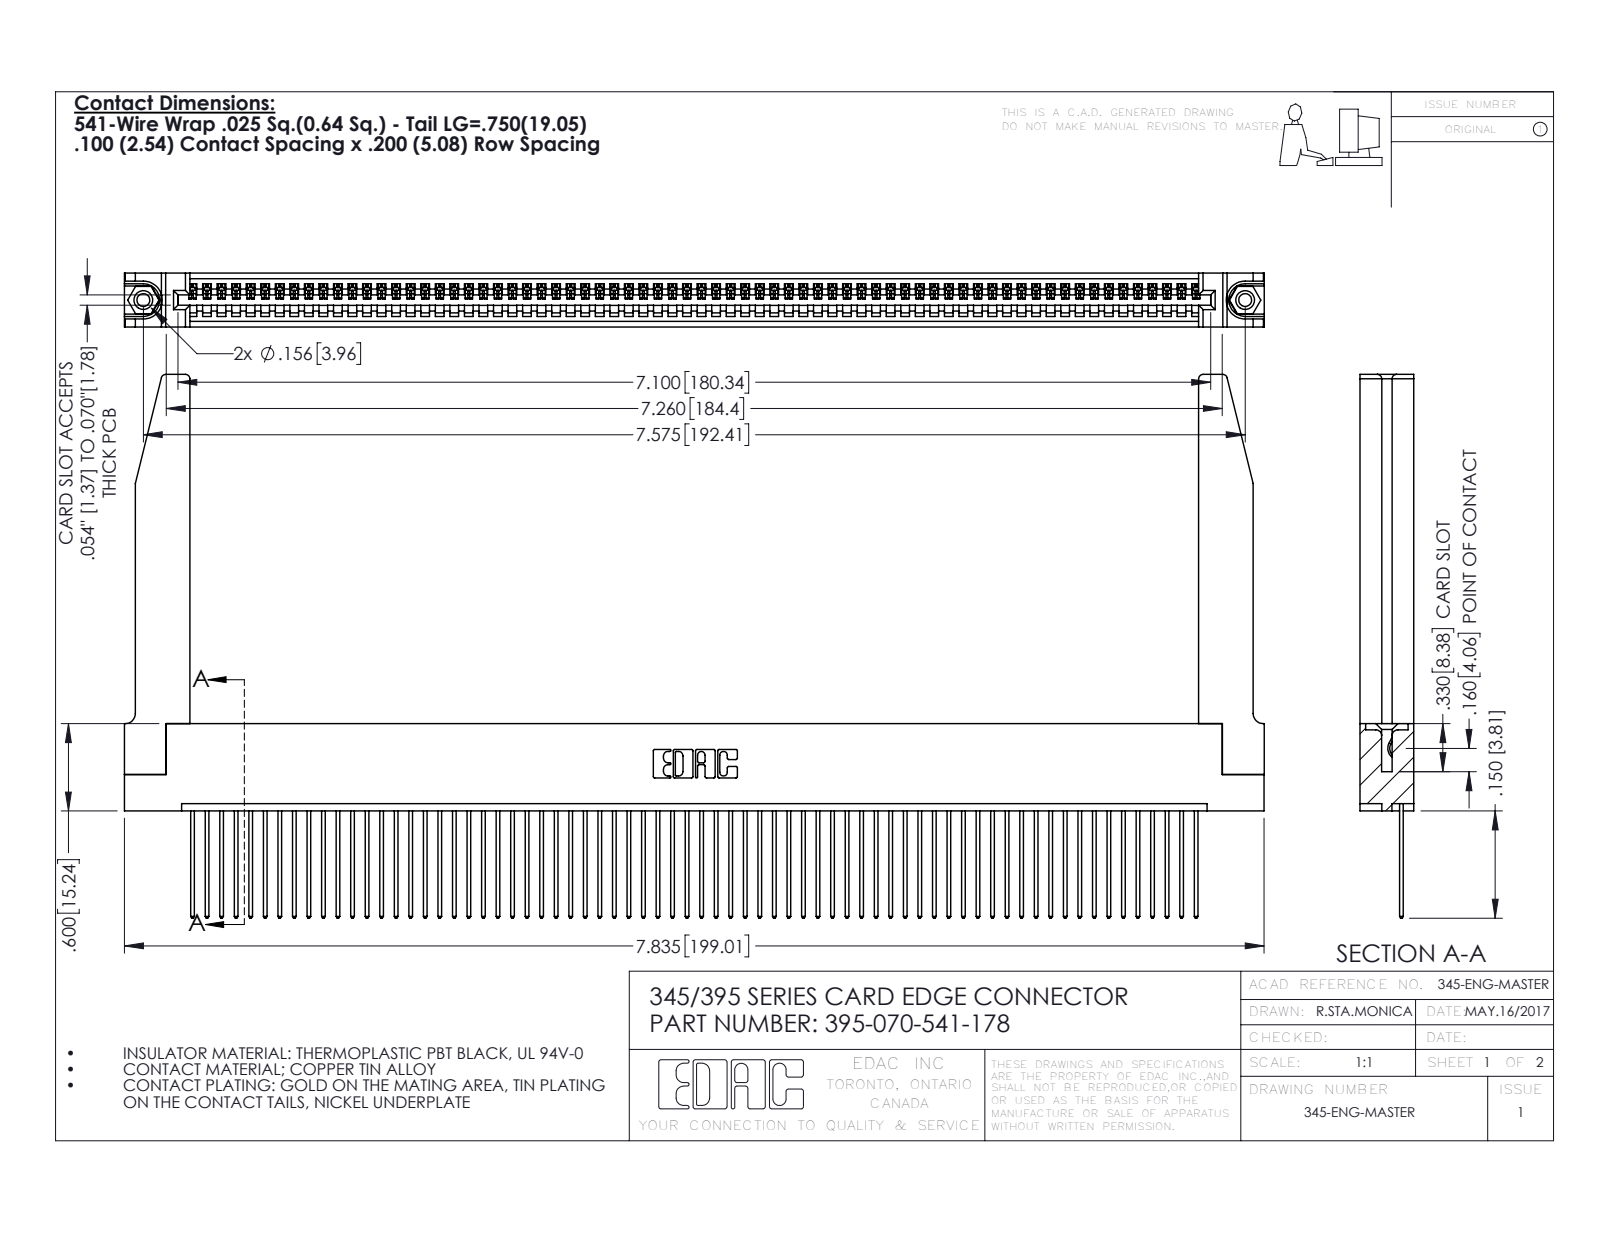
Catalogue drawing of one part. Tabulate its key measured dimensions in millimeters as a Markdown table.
| quantity | value |
| --- | --- |
| part name | 345-250-001_345-250-001-102; 345-220-078_345-220-078; 395-070-541-178; 345-292-001_345-293-141 (+1 more) |
| STEP written by | SolidWorks 2016 (CONFIG_CONTROL_DESIGN) |
| units | millimeters |
| bodies | 75 solids, 4420 faces (3022 planar, 1346 cylindrical, 52 other) |
| overall size | 199 × 94.9 × 9.4 |
| volume | 27 140 mm³ |
| surface area | 34 320 mm² |
| round holes (diameter × count) | 2.3 × 2, 3.2 × 2, 4 × 2, 1.6 × 1 |
| round bosses / shafts (diameter × count) | 3.9 × 2 |
| partial cylindrical surfaces (radius × count) | 0.2 × 140, 0.3 × 140, 0.3 × 22, 0.8 × 8, 0.2 × 6, 0.8 × 6, 0.7 × 3, 0.8 × 2 |
| main face-to-face distances | 1.8, 7.6, 9.4, 2.5, 6.9, 0.6, 5.1, 5.7, 3.8, 3.8 |
| hole center spacings | 6.9, 186.4, 192.4 |
